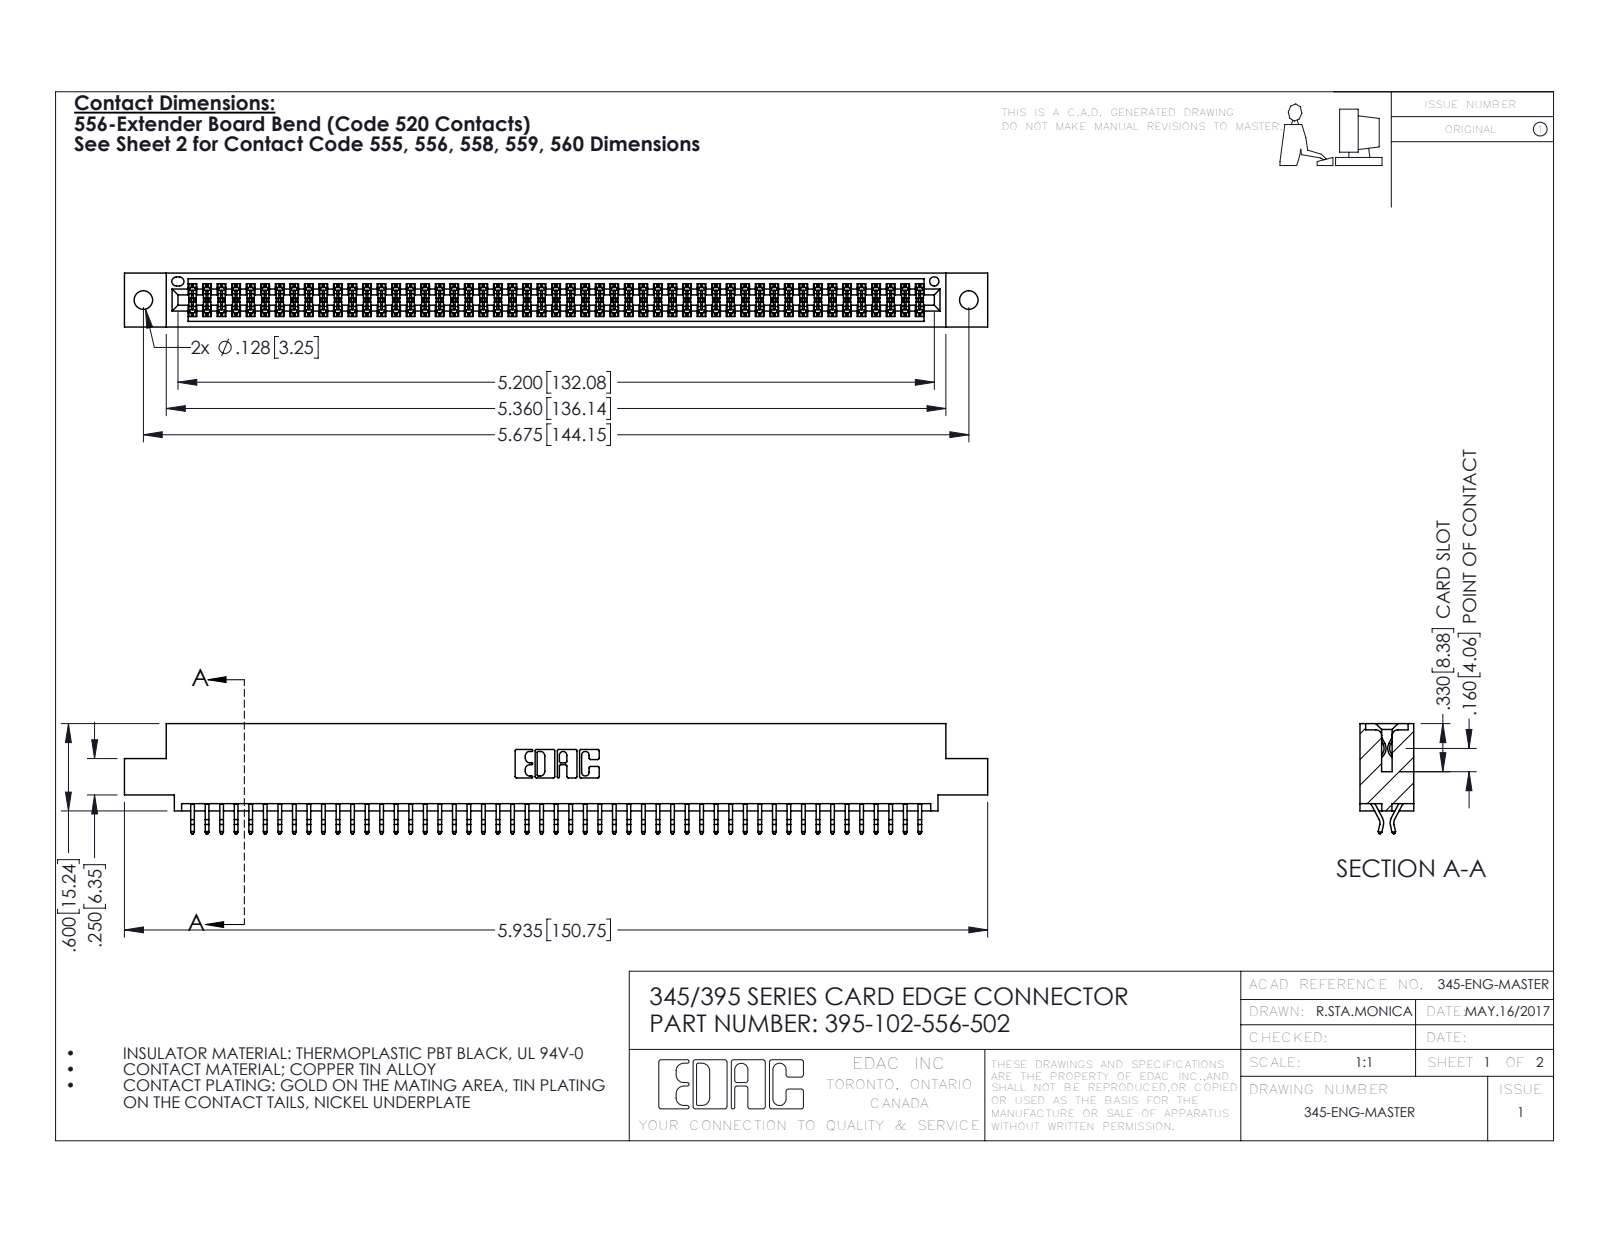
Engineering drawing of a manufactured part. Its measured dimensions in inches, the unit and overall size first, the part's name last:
Units: inches
Overall size (bounding box): 5.935 × 0.757 × 0.37
Round holes (diameter × count): ⌀0.128 ×2, ⌀0.064 ×1
Partial cylindrical surfaces — rounded edges, fillets, slot ends (radius × count): R0.006 ×153, R0.01 ×22, R0.007 ×6, R0.031 ×6, R0.026 ×3, R0.01 ×2, R0.014 ×2, R0.019 ×2
Main face-to-face distances: 0.298, 0.072, 0.37, 0.2, 0.025, 0.098, 0.272, 0.225, 0.175, 0.149
Hole centre spacings: 0.27, 5.439, 5.675
Volume: 0.892 in³ · Surface area: 33.33 in²
Bodies: 103 solids, 5842 faces (3858 planar, 1984 cylindrical, 0 other)
Part name (STEP PRODUCT): 345 Part_0.110 Offset - 0.128 Dia; 345-292-001_556 Tail; 395-102-556-502
STEP written by: SolidWorks 2016 (CONFIG_CONTROL_DESIGN)
